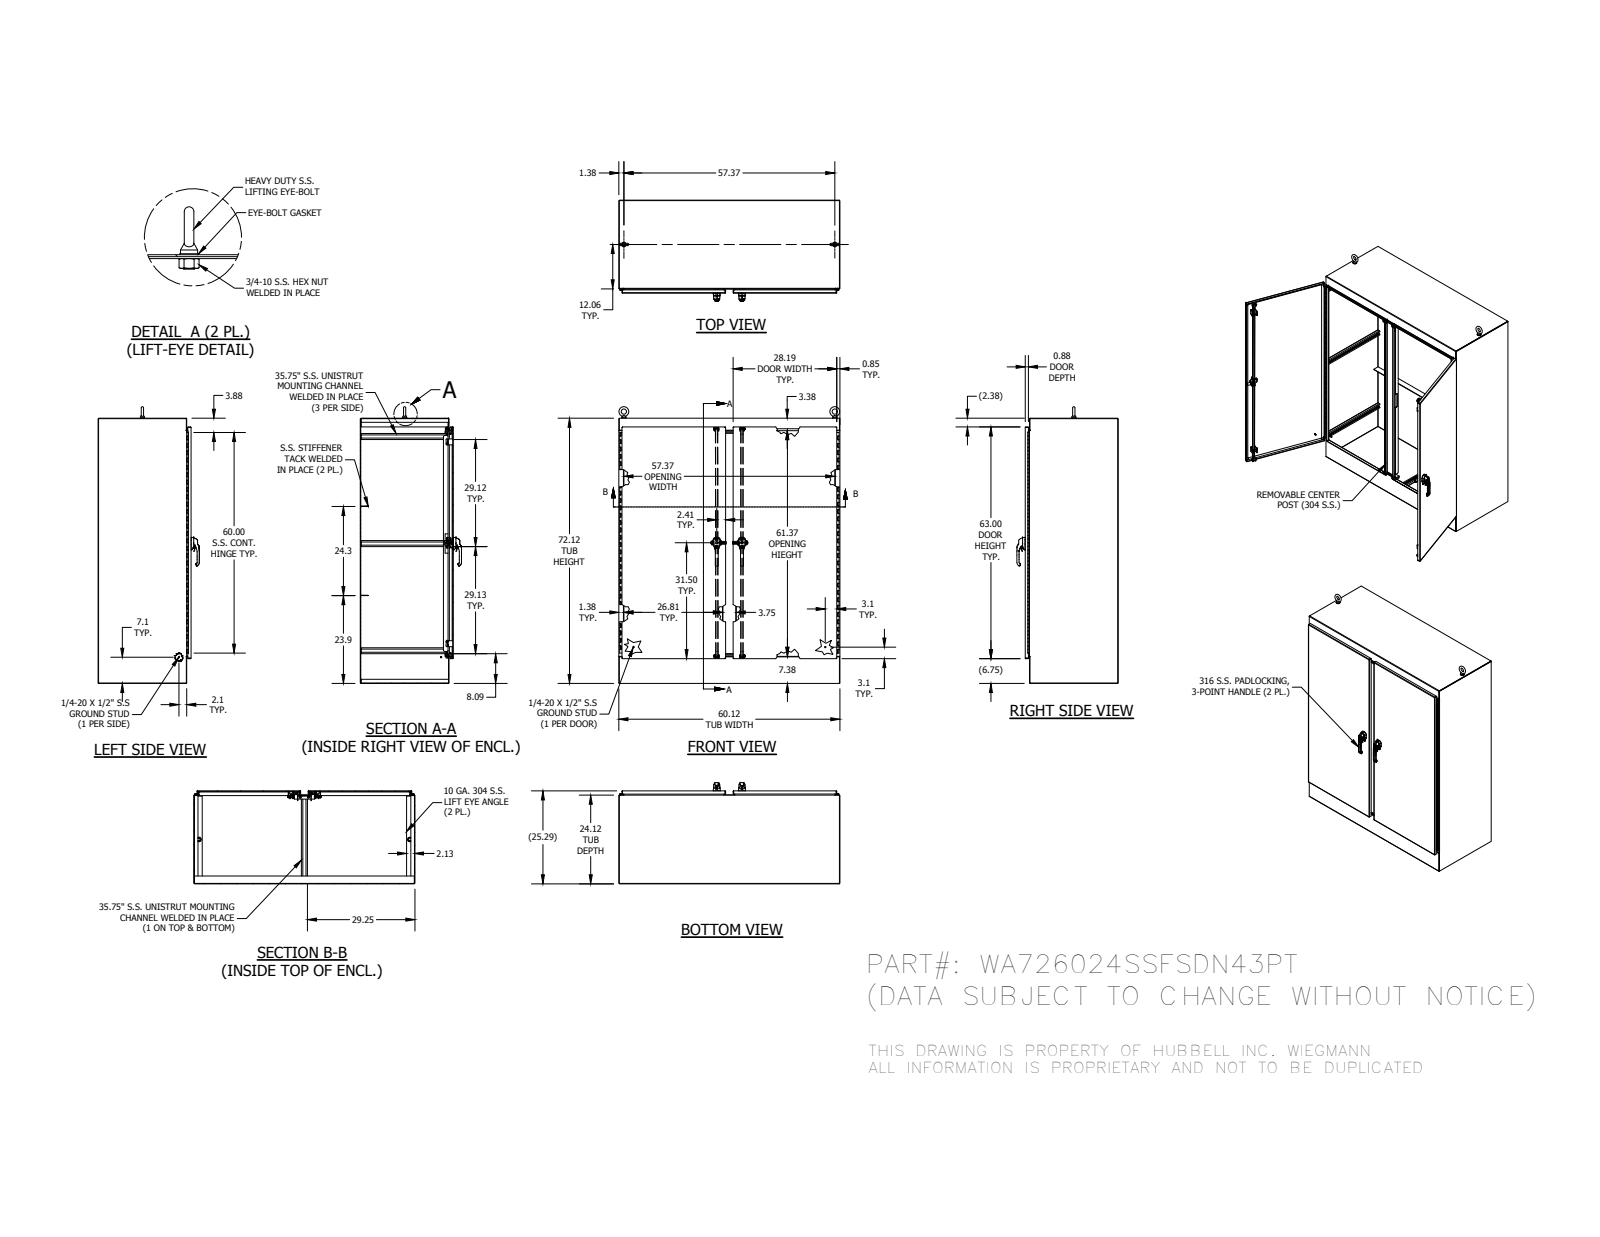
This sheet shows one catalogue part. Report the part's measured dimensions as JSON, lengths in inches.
{"part_name": "DIN985_M10; HFW372182; WA7260SSFSDN43PTFIP; HFW3026 (+8 more)", "step_written_by": "SolidWorks 2014 (AUTOMOTIVE_DESIGN)", "units": "inches", "bodies": {"solids": 133, "faces": 7024, "planar": 2638, "cylindrical": 2690, "other": 1696}, "overall_size": [75.248, 60.125, 27.541], "volume_in3": 2273, "surface_area_in2": 37080, "round_holes": [[0.262, 16], [0.375, 16], [0.187, 8], [0.213, 6], [0.281, 6], [0.25, 5], [0.196, 4], [0.241, 4], [0.252, 4], [0.281, 4], [0.315, 4], [0.4, 4]], "round_bosses_or_shafts": [[0.25, 7], [0.533, 6], [0.236, 6], [1, 5], [0.563, 4], [0.531, 4], [0.5, 4], [0.438, 4]], "partial_cylinders_radius": [[0.02, 352], [0.012, 214], [0.019, 44], [0.125, 44], [0.05, 34], [0.079, 28], [0.025, 24], [0.059, 24]], "face_to_face_distances": [0.125, 0.125, 25.167, 60, 72, 24, 1.167, 59.875, 25.165, 25.04], "hole_center_spacings": [54.49, 55.24, 20, 0.38, 0.38, 6.667, 0.76, 13.333]}
